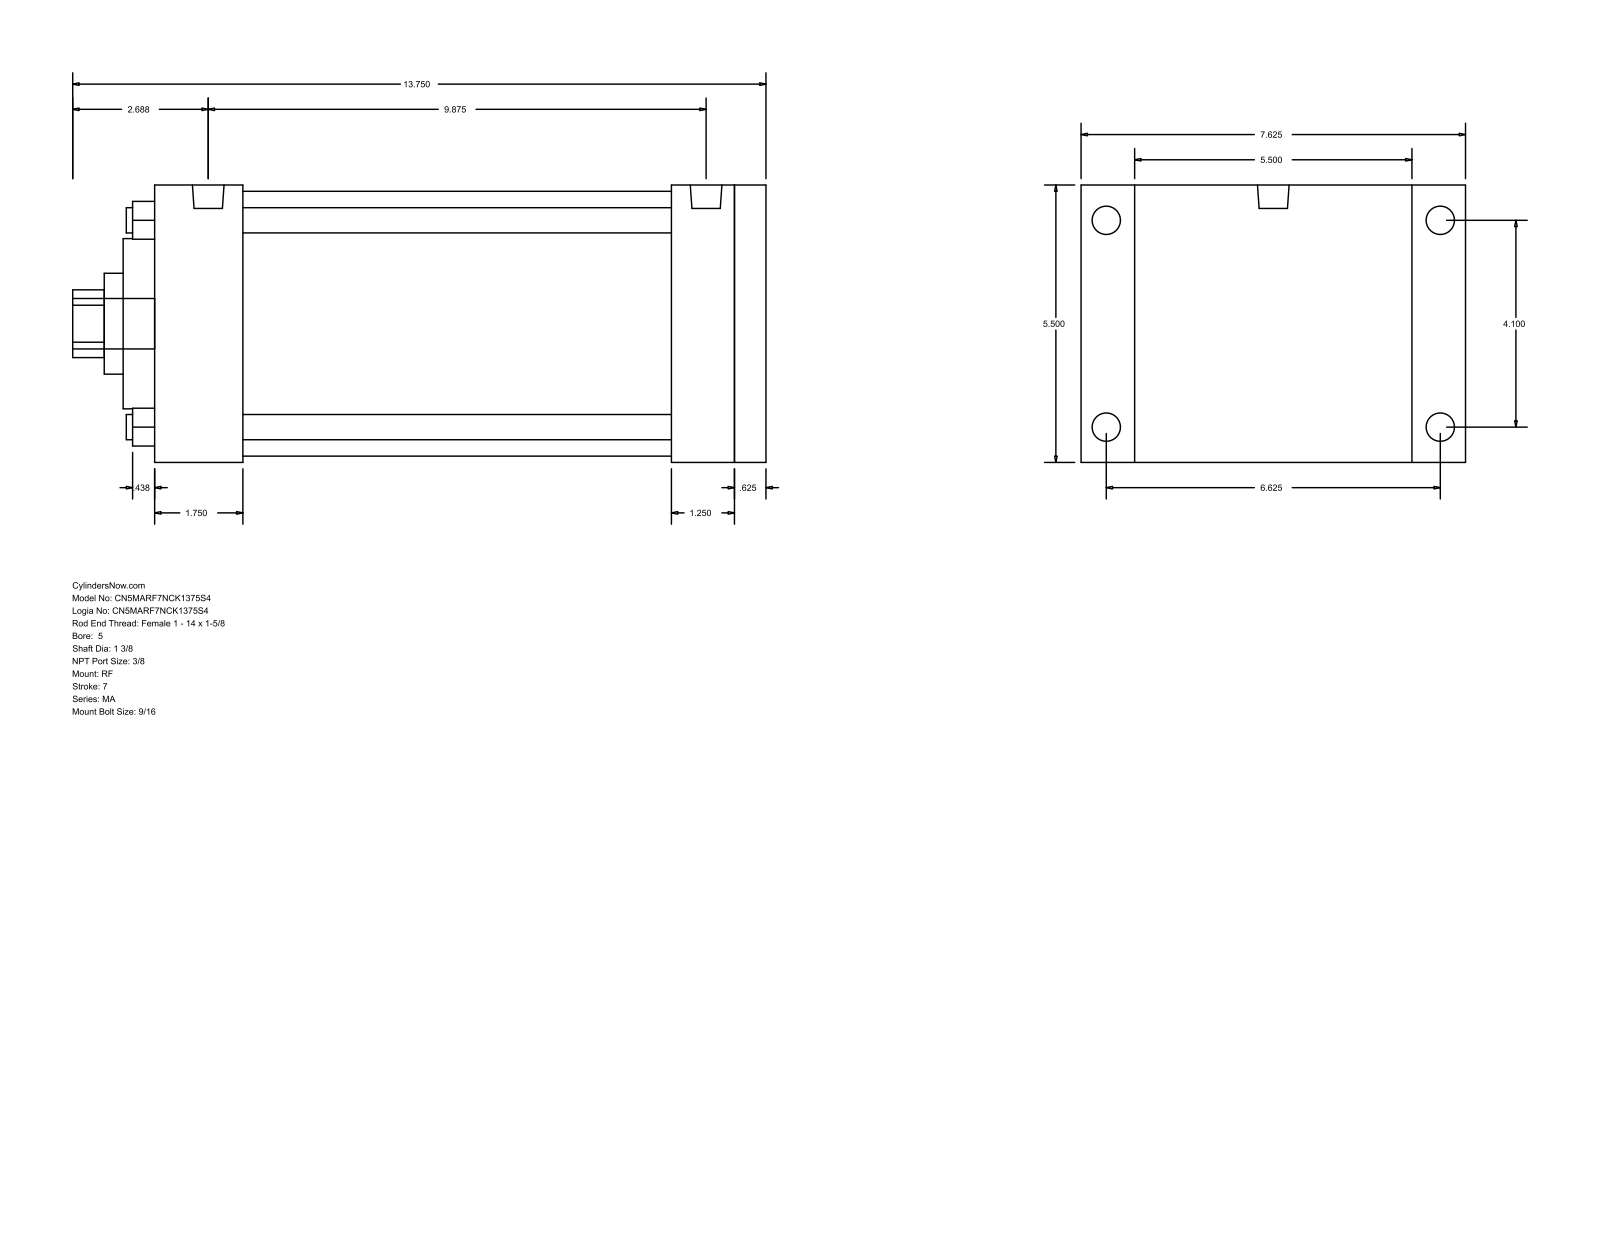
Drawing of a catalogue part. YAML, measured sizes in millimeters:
part_name: "MA_RF__0500_1.375"
step_written_by: "GSSL Pune (CONFIG_CONTROL_DESIGN)"
units: millimeters
bodies: {solids: 0, faces: 94, planar: 65, cylindrical: 29, other: 0}
overall_size: [349.25, 193.68, 139.7]
round_holes:
  - {diameter: 12.7, count: 4}
  - {diameter: 34.92, count: 1}
  - {diameter: 50.8, count: 1}
  - {diameter: 85.72, count: 1}
  - {diameter: 133.35, count: 1}
round_bosses_or_shafts:
  - {diameter: 14.29, count: 4}
  - {diameter: 11.11, count: 4}
  - {diameter: 15.93, count: 2}
  - {diameter: 25.4, count: 1}
partial_cylinders:
  - {radius: 17.06, count: 1}
face_to_face_distances: [139.7, 307.98, 15.87, 292.11, 44.45, 247.66, 263.53, 260.35, 215.9, 31.76]
hole_center_spacings: [73.64, 104.14, 147.28]
